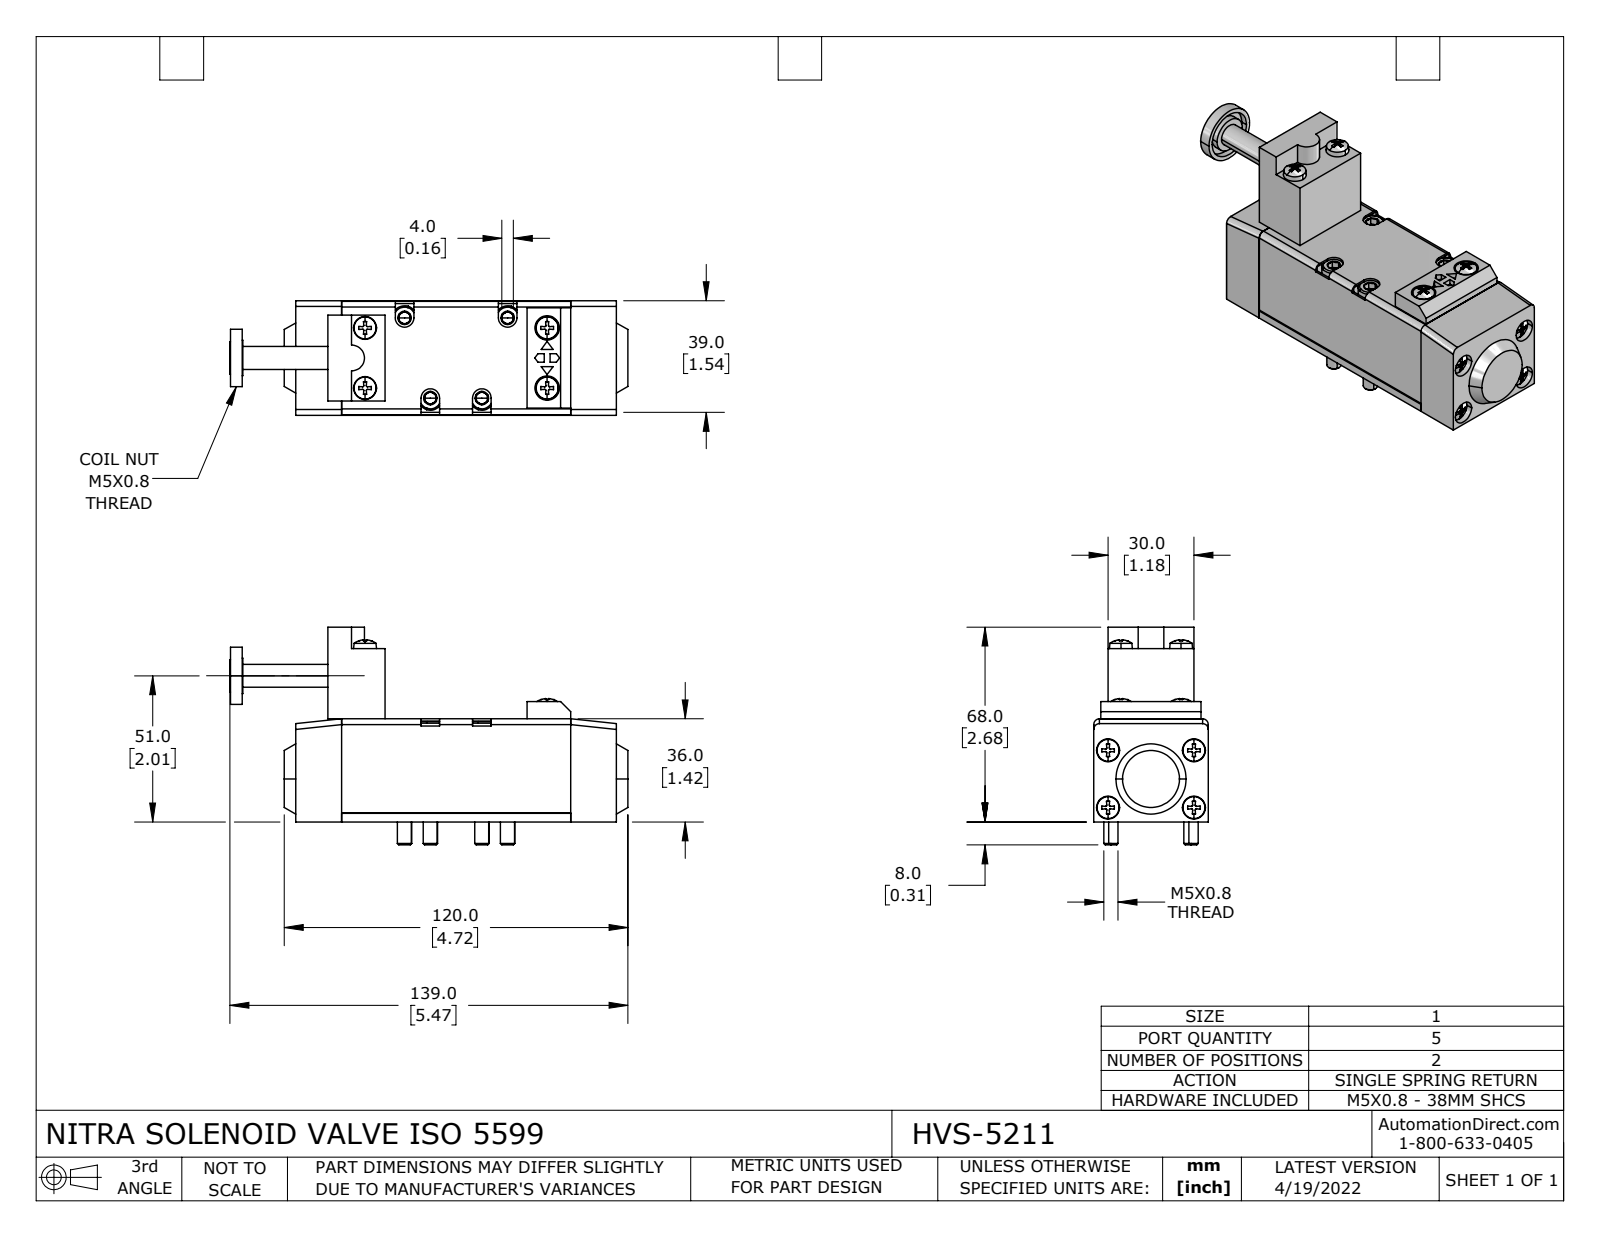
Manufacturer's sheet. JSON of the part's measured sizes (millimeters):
{"part_name": "HVS-5211", "step_written_by": "SolidWorks 2021 (CONFIG_CONTROL_DESIGN)", "units": "millimeters", "bodies": {"solids": 21, "faces": 855, "planar": 448, "cylindrical": 147, "other": 260}, "overall_size": [139, 76, 40], "volume_mm3": 183000, "surface_area_mm2": 48990, "round_holes": [[3.3, 8], [5.5, 4], [8, 4], [4.1, 2], [4.2, 2], [8.5, 2], [5, 1], [16.9, 1]], "round_bosses_or_shafts": [[4, 8], [8.5, 4], [5, 4], [20, 1], [12.4, 1], [11.3, 1], [8, 1]], "partial_cylinders_radius": [[2, 6], [3.3, 4], [5, 4], [4.5, 1]], "face_to_face_distances": [36, 80, 39.8, 39.6, 4.8, 4, 40, 20, 16, 84.8], "hole_center_spacings": [14.2, 20, 21, 23.1, 28.1, 29.4, 30, 30]}
